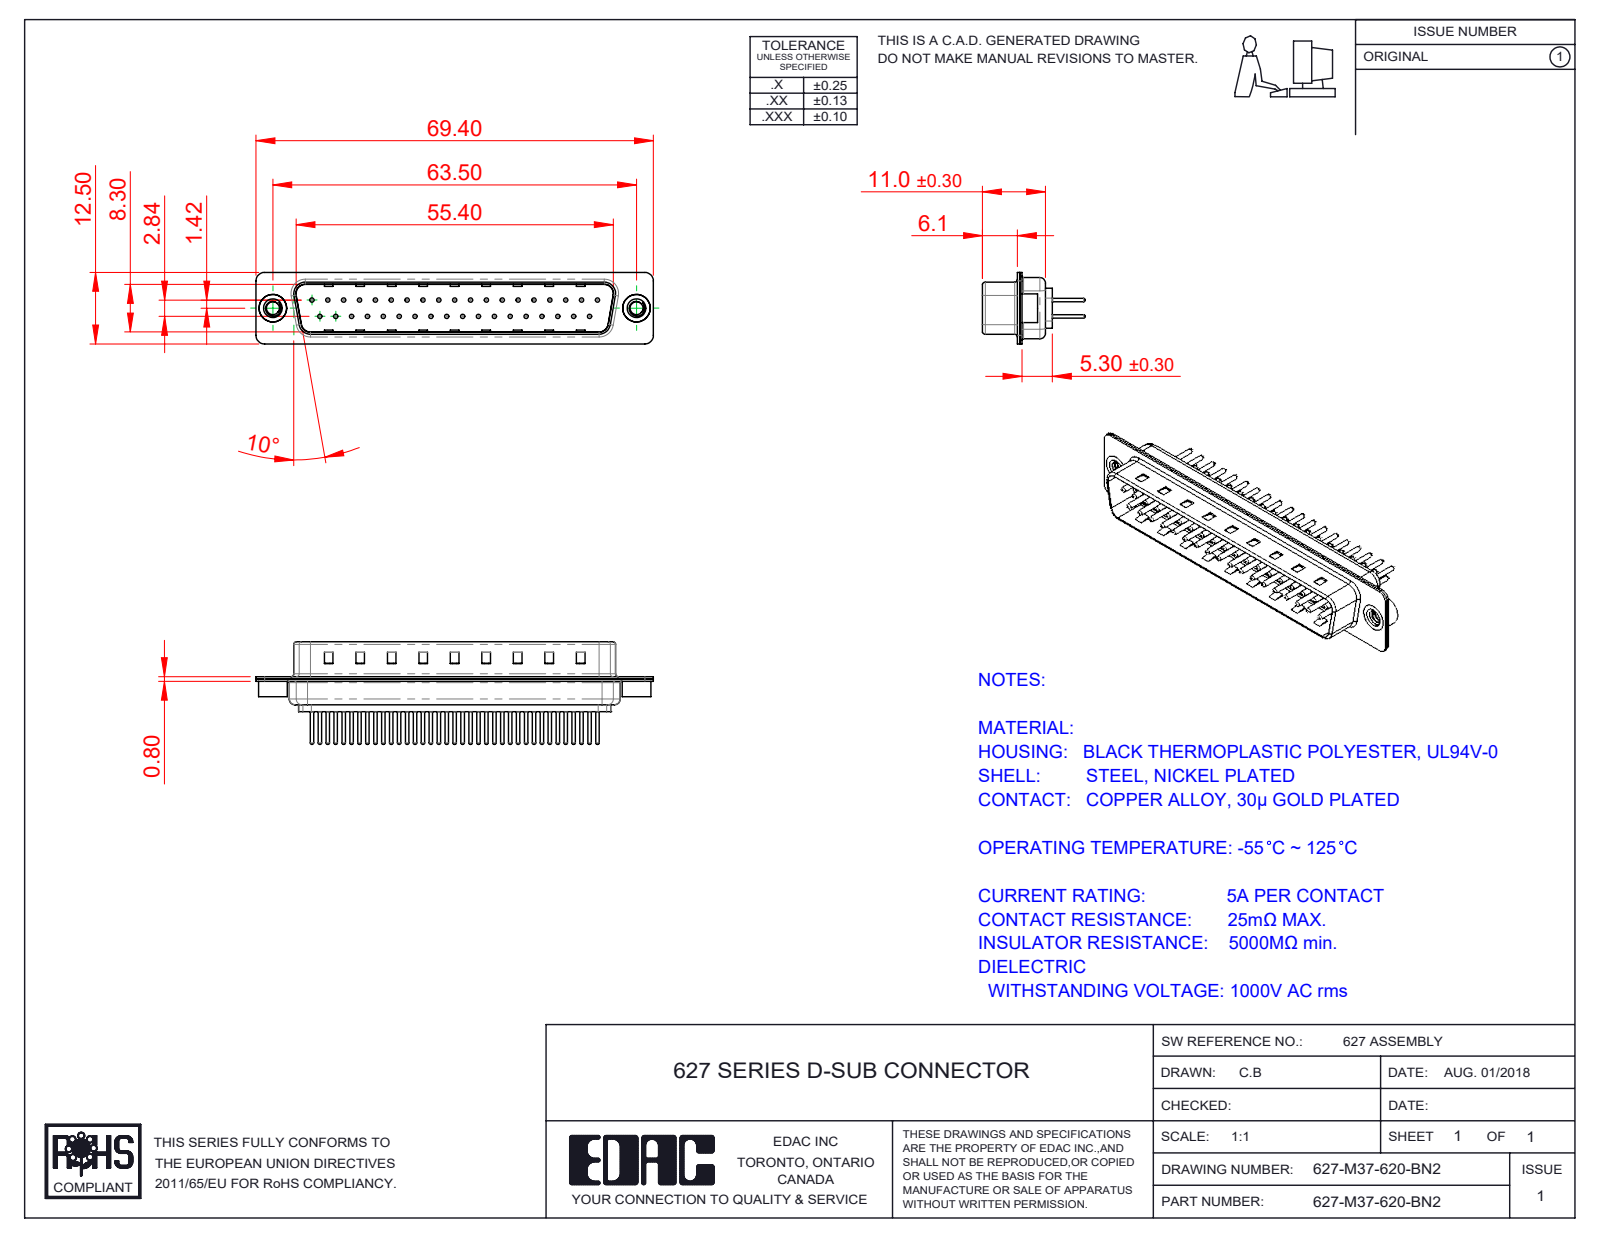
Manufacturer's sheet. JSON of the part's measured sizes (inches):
{"part_name": "627-M37-620-BN2; 627M Shell Rear_37 Contacts; 627M 4-40 Threaded Rivet; 627M Contact Row 2_20 (+3 more)", "step_written_by": "SolidWorks 2020 (CONFIG_CONTROL_DESIGN)", "units": "inches", "bodies": {"solids": 42, "faces": 1781, "planar": 462, "cylindrical": 659, "other": 660}, "overall_size": [2.732, 0.705, 0.492], "volume_in3": 0.23, "surface_area_in2": 14.37, "round_holes": [[0.03, 37], [0.063, 37], [0.079, 37], [0.089, 2], [0.157, 2], [0.189, 2]], "round_bosses_or_shafts": [[0.059, 37], [0.024, 37], [0.197, 2], [0.193, 2]], "partial_cylinders_radius": [[0.059, 16], [0.079, 12], [0.02, 8], [0.063, 8], [0.01, 4], [0.024, 4], [0.026, 4], [0.035, 4]], "face_to_face_distances": [0.016, 0.031, 0.374, 0.358, 0.343, 0.39, 0.047, 0.224, 0.03, 0.014], "hole_center_spacings": [0.109, 0.218, 0.124, 0.327, 0.436, 0.545, 0.654, 0.763]}
